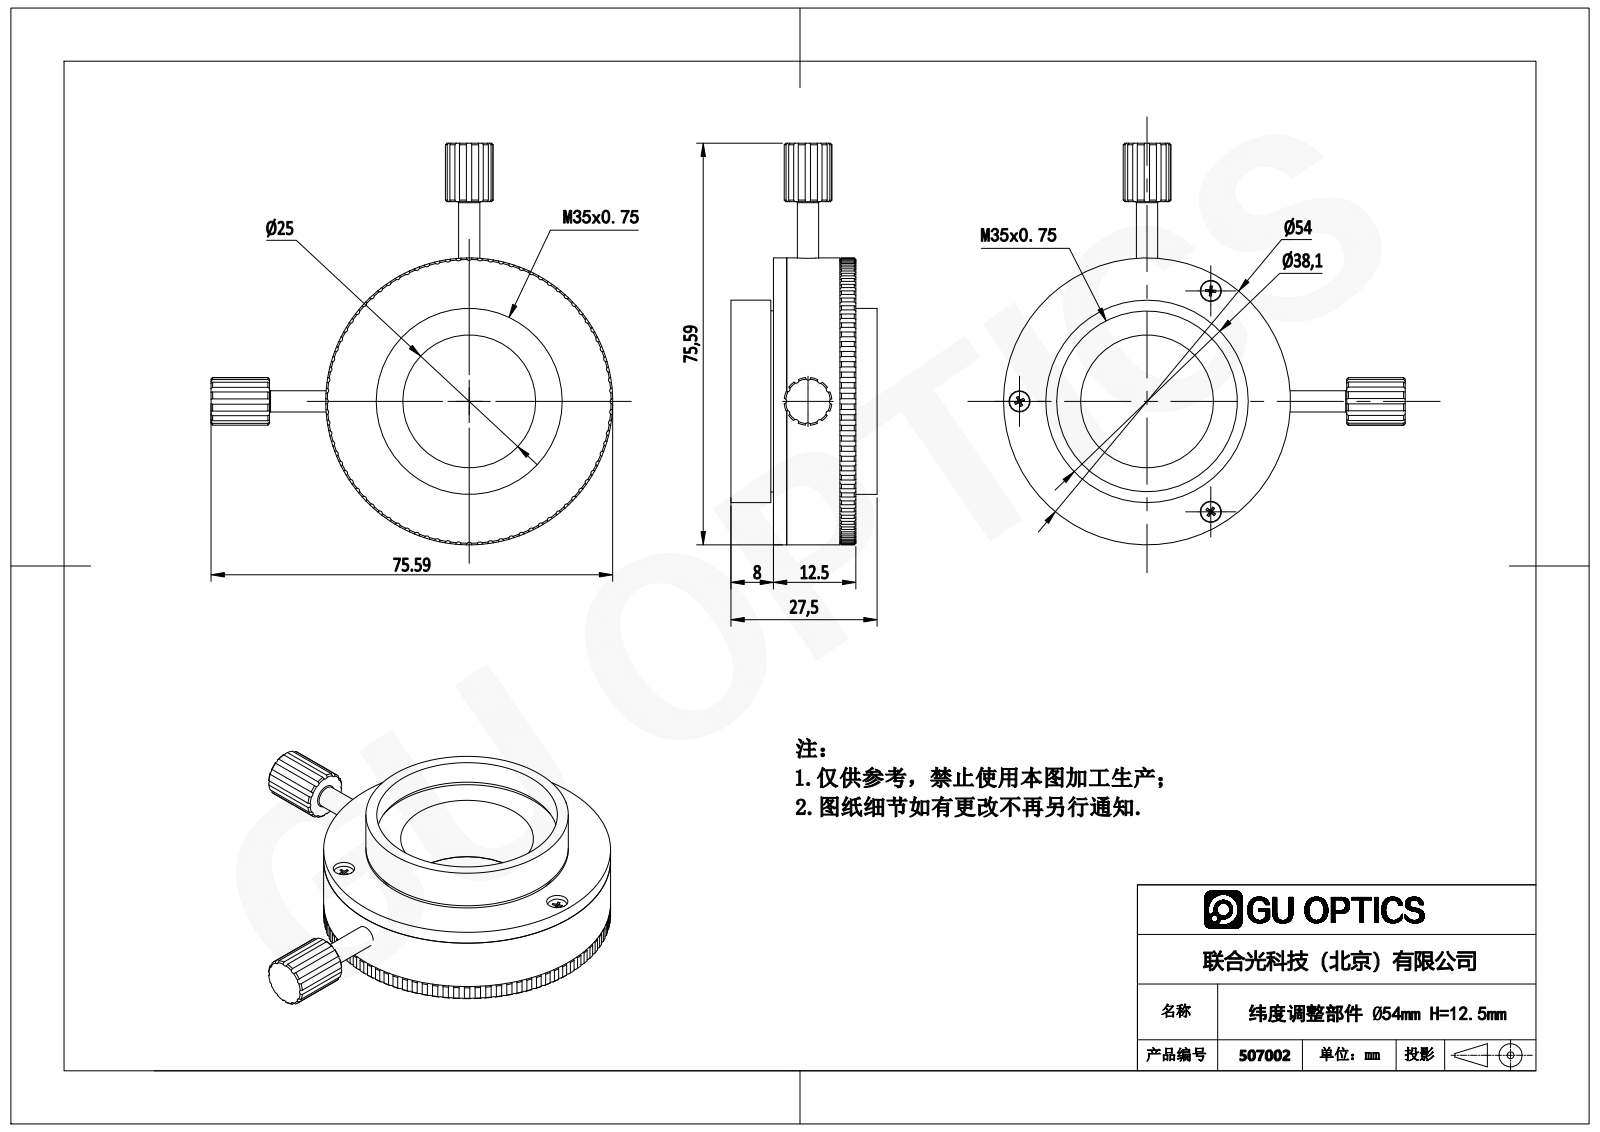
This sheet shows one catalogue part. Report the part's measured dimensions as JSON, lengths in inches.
{"part_name": "507002", "step_written_by": "SolidWorks 2020 (CONFIG_CONTROL_DESIGN)", "units": "inches", "bodies": {"solids": 10, "faces": 685, "planar": 70, "cylindrical": 347, "other": 268}, "overall_size": [2.976, 2.976, 1.083], "volume_in3": 1.9, "surface_area_in2": 35.18, "round_holes": [[0.063, 3], [0.094, 3], [0.157, 3], [0.13, 2], [0.039, 1], [0.205, 1], [0.244, 1], [0.984, 1], [1.339, 1], [1.386, 1], [1.5, 1], [1.772, 1]], "round_bosses_or_shafts": [[0.079, 3], [0.055, 3], [0.157, 2], [2.126, 1], [1.614, 1], [1.378, 1], [1.343, 1], [0.236, 1]], "partial_cylinders_radius": [[0.02, 108], [0.177, 2]], "face_to_face_distances": [0.394, 0.079, 0.315, 0.512, 0.197, 0.118, 0.098, 0.413, 0.61, 0.492], "hole_center_spacings": [0.945, 1.637]}
